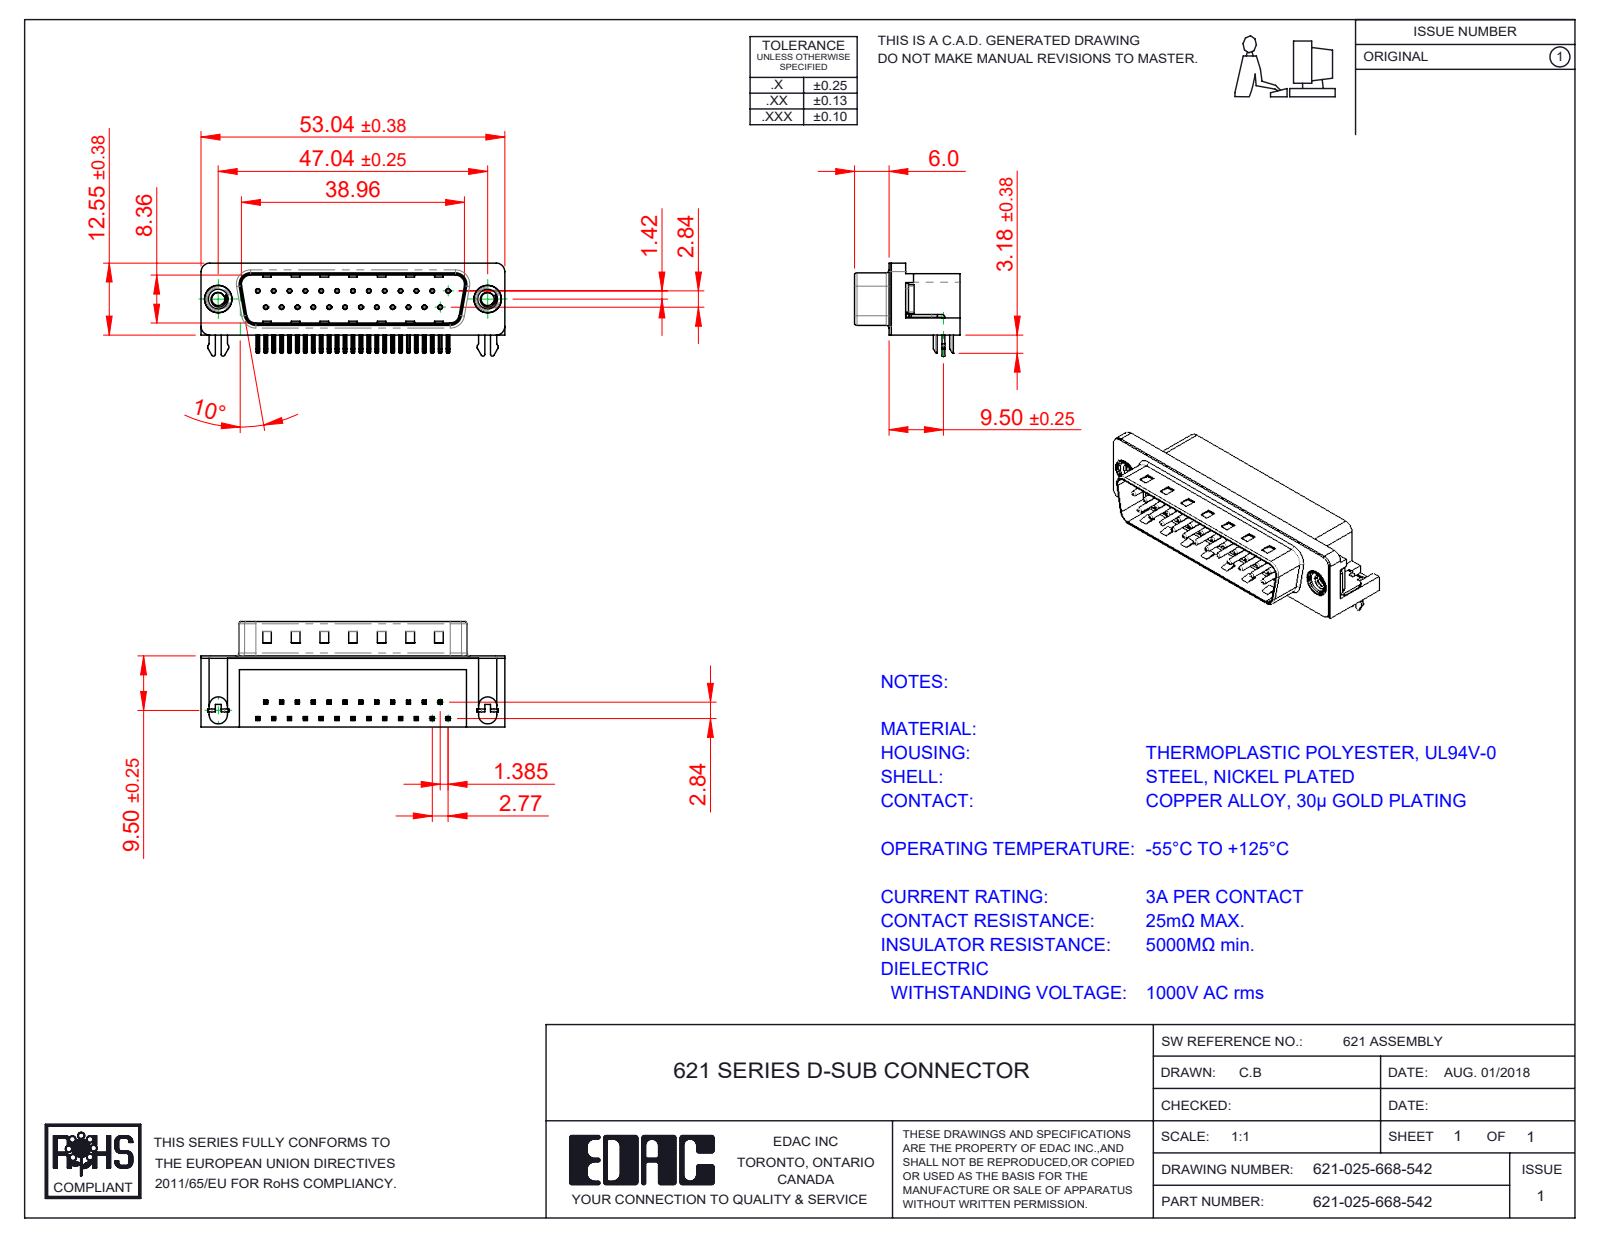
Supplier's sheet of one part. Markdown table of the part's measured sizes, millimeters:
| quantity | value |
| --- | --- |
| part name | 621 Shell_25 Socket; 621 Housing_25 Socket; 621 Contact Bottom; 621-025-668-542 (+3 more) |
| STEP written by | SolidWorks 2016 (CONFIG_CONTROL_DESIGN) |
| units | millimeters |
| bodies | 31 solids, 2383 faces (1447 planar, 665 cylindrical, 271 other) |
| overall size | 53.04 × 18.4 × 16.25 |
| volume | 6 358 mm³ |
| surface area | 7 758 mm² |
| round holes (diameter × count) | 0.35 × 25, 0.8 × 25, 2 × 2, 2.26 × 2, 4 × 2, 4.8 × 2, 5 × 2 |
| round bosses / shafts (diameter × count) | 0.75 × 25, 4.9 × 2, 4.75 × 2, 3.9 × 2, 3 × 2 |
| partial cylindrical surfaces (radius × count) | 0.25 × 112, 0.12 × 50, 1 × 16, 0.5 × 9, 1.6 × 8, 1.5 × 7, 0.9 × 4, 2 × 4 |
| main face-to-face distances | 0.4, 12, 10.35, 2.1, 8.76, 10.46, 1.7, 10.86, 12.4, 9 |
| hole center spacings | 3.16, 2.77, 5.54, 8.31, 11.08, 13.85, 16.62, 5.03 |
